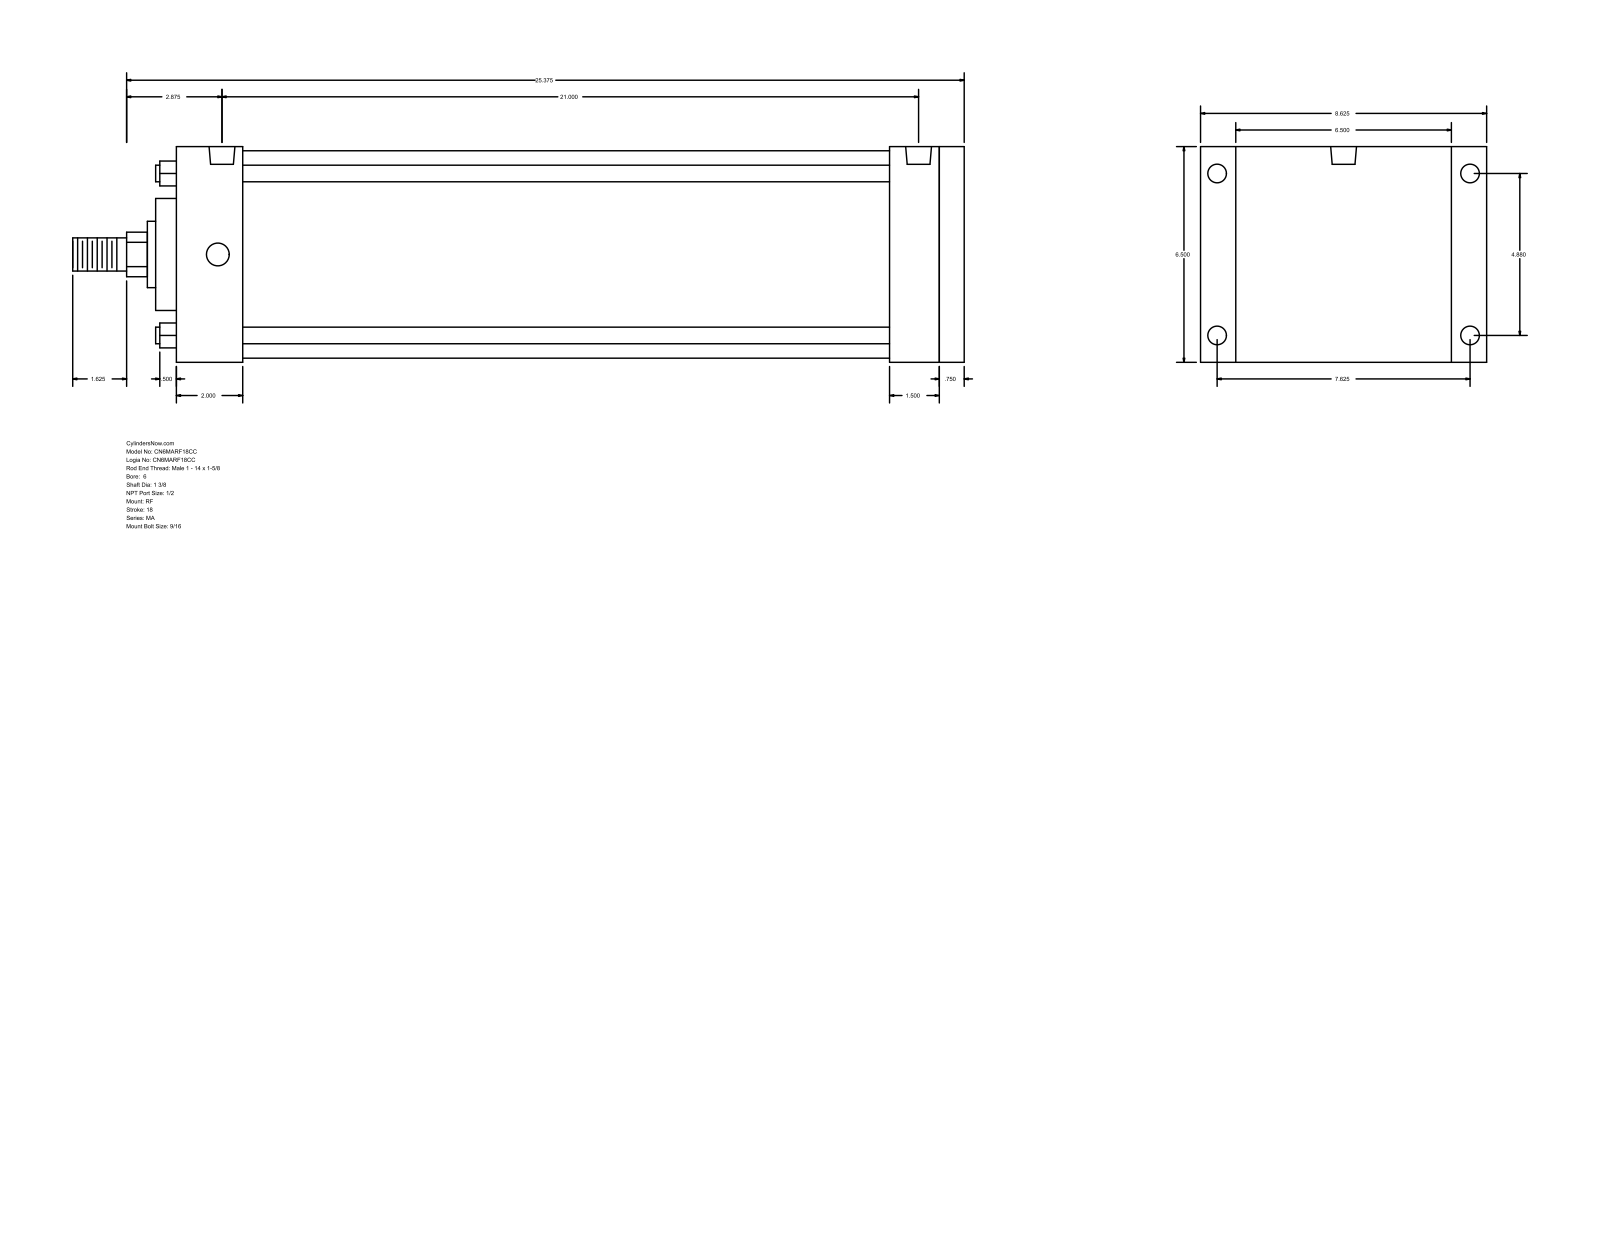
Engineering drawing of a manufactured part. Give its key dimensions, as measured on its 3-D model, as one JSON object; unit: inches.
{"part_name": "MA_RF__0600_1.375", "step_written_by": "GSSL Pune (CONFIG_CONTROL_DESIGN)", "units": "inches", "bodies": {"solids": 0, "faces": 94, "planar": 65, "cylindrical": 29, "other": 0}, "overall_size": [27, 8.625, 6.5], "round_holes": [[0.563, 4], [0.687, 4], [0.778, 2]], "round_bosses_or_shafts": [[0.5, 4], [6.25, 1], [3.375, 1], [2, 1], [1.375, 1], [1, 1]], "partial_cylinders_radius": [[0.672, 1]], "face_to_face_distances": [6.5, 23.875, 23.125, 0.75, 1.5, 2, 21.125, 21.875, 21.625, 19.625], "hole_center_spacings": [4.88, 7.625, 9.053, 21.125, 0.125, 21]}
